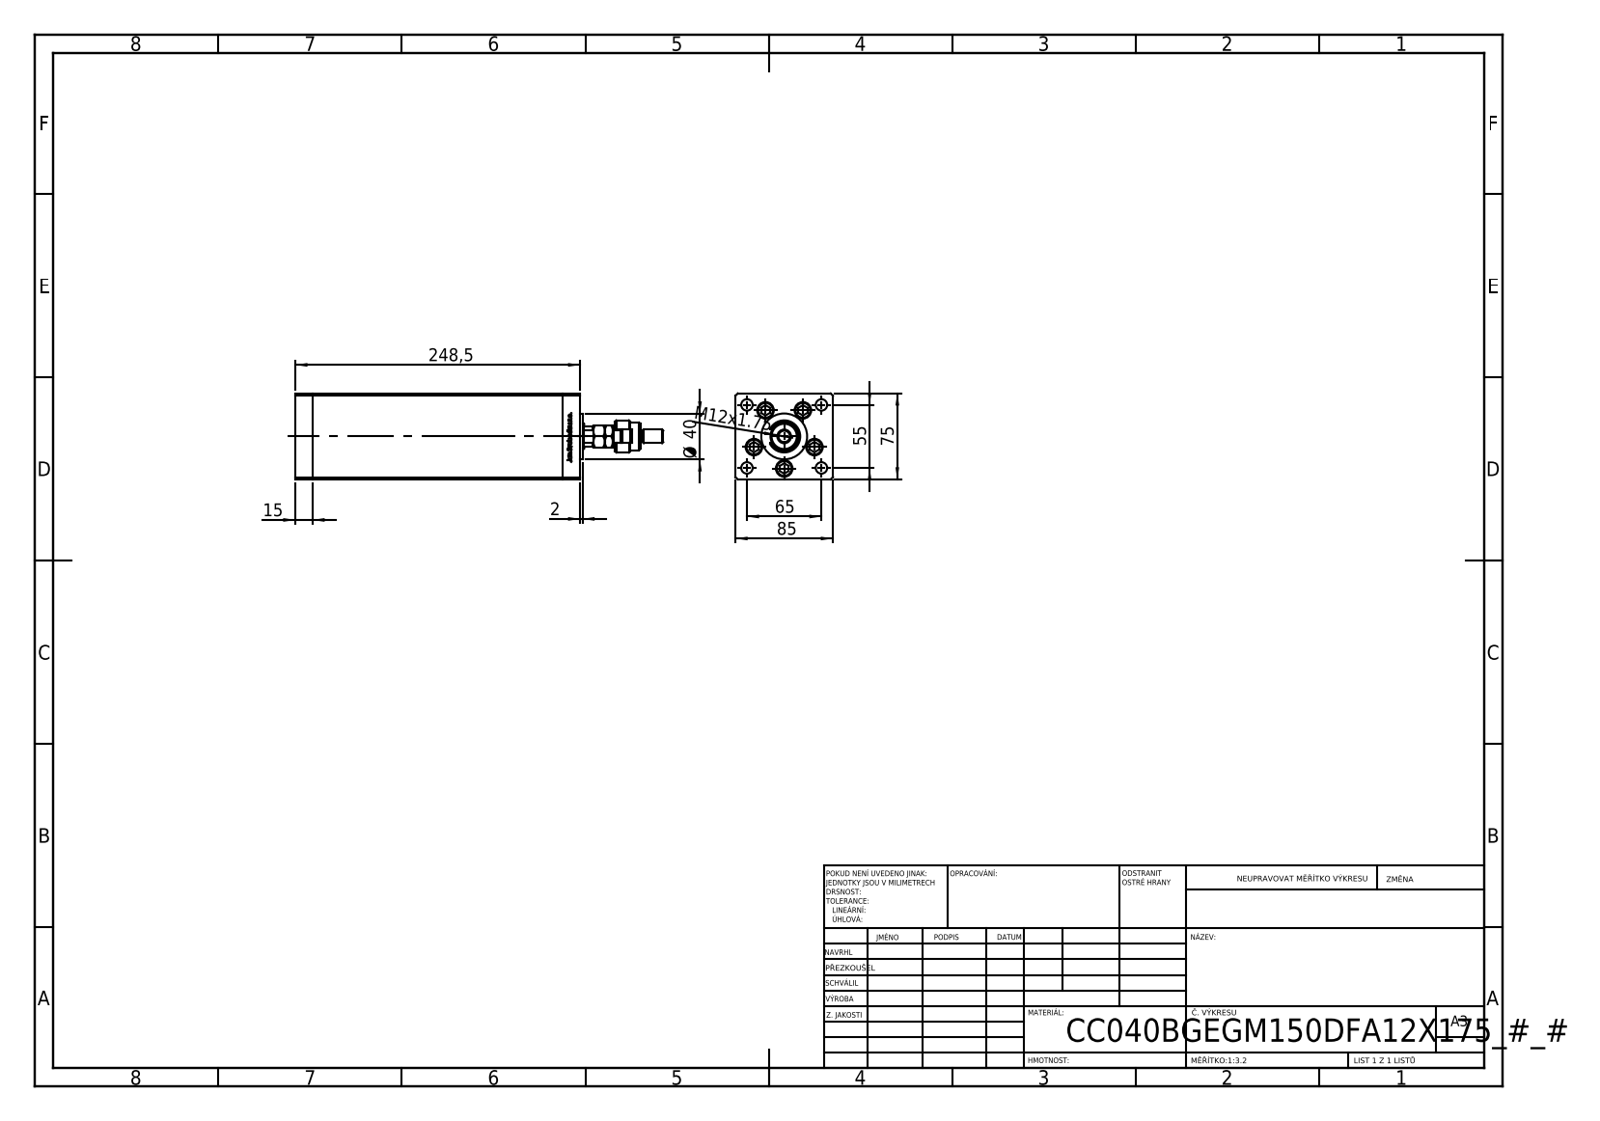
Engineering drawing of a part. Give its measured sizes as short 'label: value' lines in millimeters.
name: FEMALE_PART_FOR_DFA; V220C_FRONT_B; MFA; V220C_B MIDDLE (+3 more)
written by: SolidWorks 2019 (CONFIG_CONTROL_DESIGN)
unit: mm
bodies: 16 solids, 1270 faces (492 planar, 160 cylindrical, 618 other)
size: 321 × 85 × 75
volume: 1 400 000 mm³; area: 205 024 mm²
holes: 5× ⌀11, 5× ⌀14.5, 4× ⌀10, 2× ⌀2, 2× ⌀13.16, 1× ⌀13.5, 1× ⌀22
bosses: 5× ⌀8, 1× ⌀40, 1× ⌀28, 1× ⌀24, 1× ⌀18, 1× ⌀12, 1× ⌀11, 1× ⌀10
rounds: 2× R0.93, 1× R9.75, 1× R10.5
face distances: 85, 75, 15, 218.5, 233.5, 248.5, 34.25, 68.5, 64.5, 10.5
hole spacings: 28, 42.57, 16.86, 19.17, 32.33, 32.5, 33.63, 37.33
